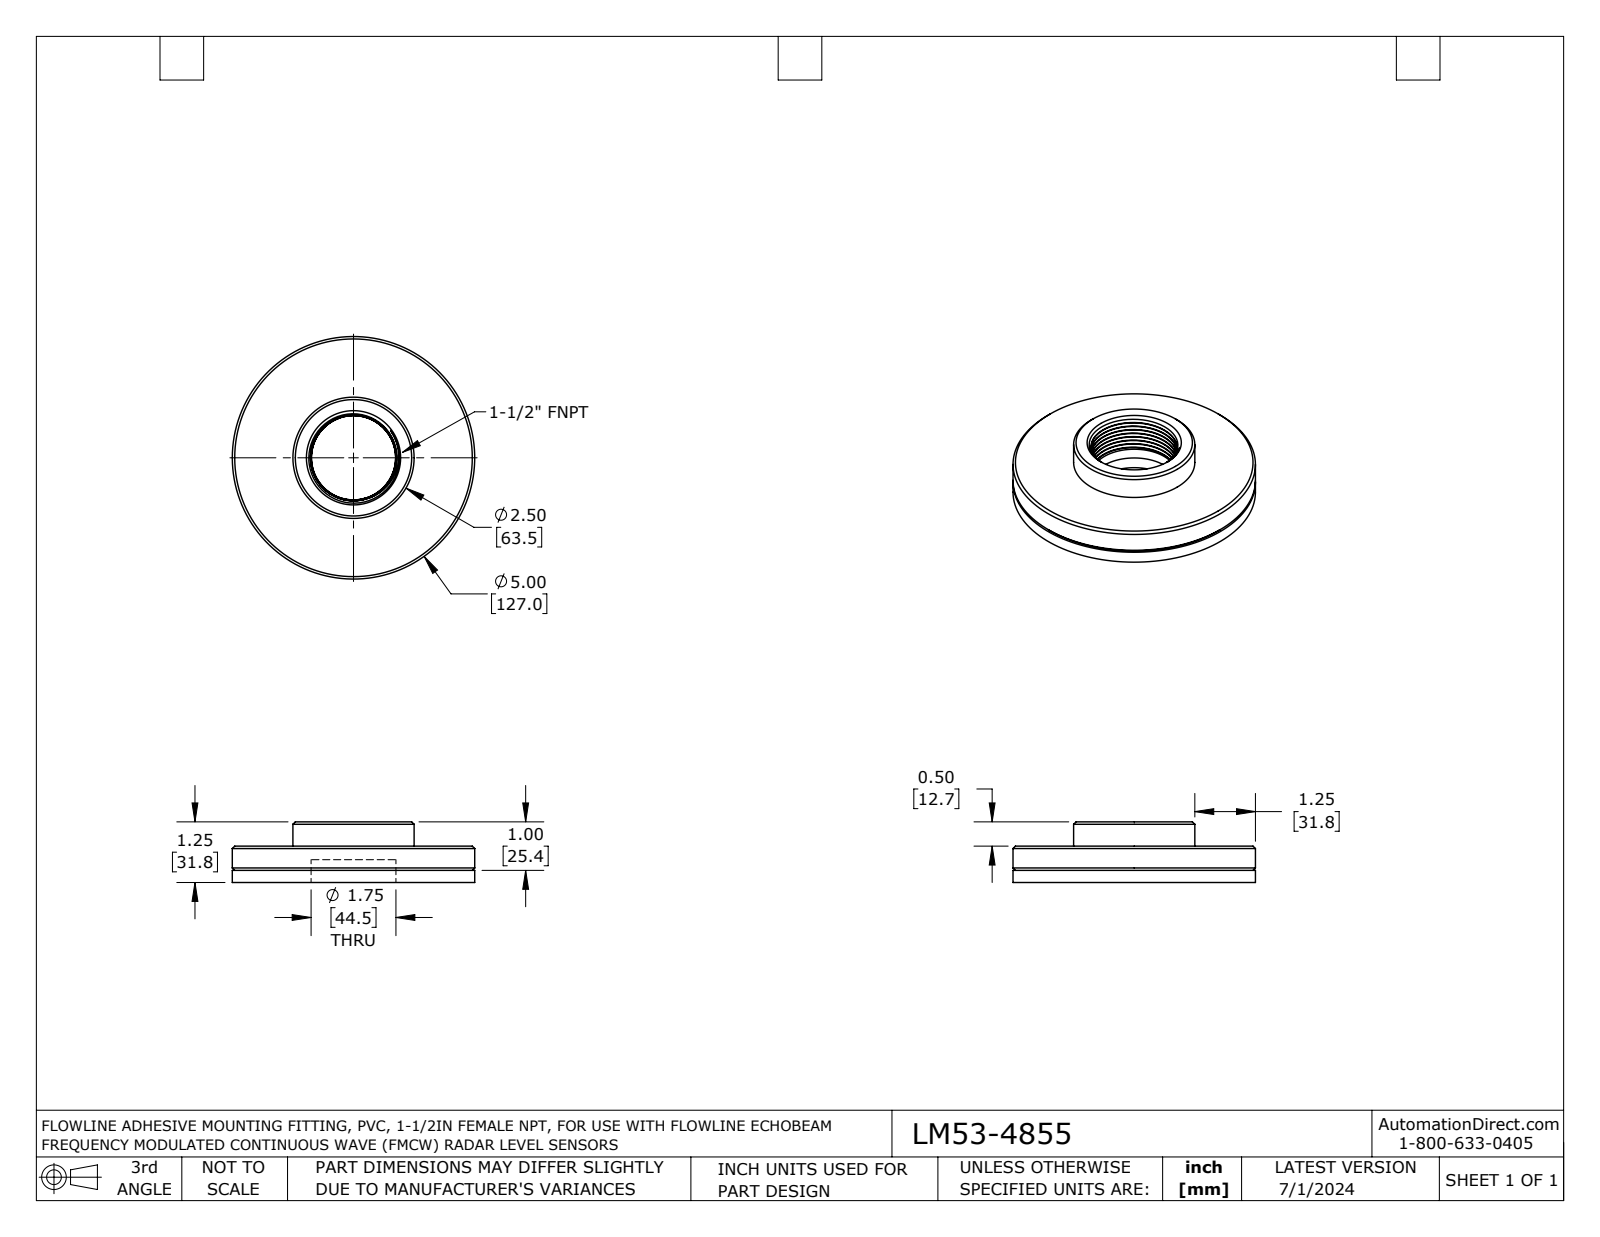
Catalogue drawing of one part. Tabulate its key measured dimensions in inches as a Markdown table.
| quantity | value |
| --- | --- |
| part name | LM53-4855 |
| STEP written by | SolidWorks 2021 (AUTOMOTIVE_DESIGN) |
| units | inches |
| bodies | 2 solids, 48 faces (5 planar, 10 cylindrical, 33 other) |
| overall size | 5 × 5 × 1.25 |
| volume | 13.98 in³ |
| surface area | 93.23 in² |
| round holes (diameter × count) | 1.736 × 1, 1.75 × 1 |
| round bosses / shafts (diameter × count) | 5 × 1, 2.5 × 1 |
| main face-to-face distances | 0.25, 0.5, 0.75, 1.25, 1 |
